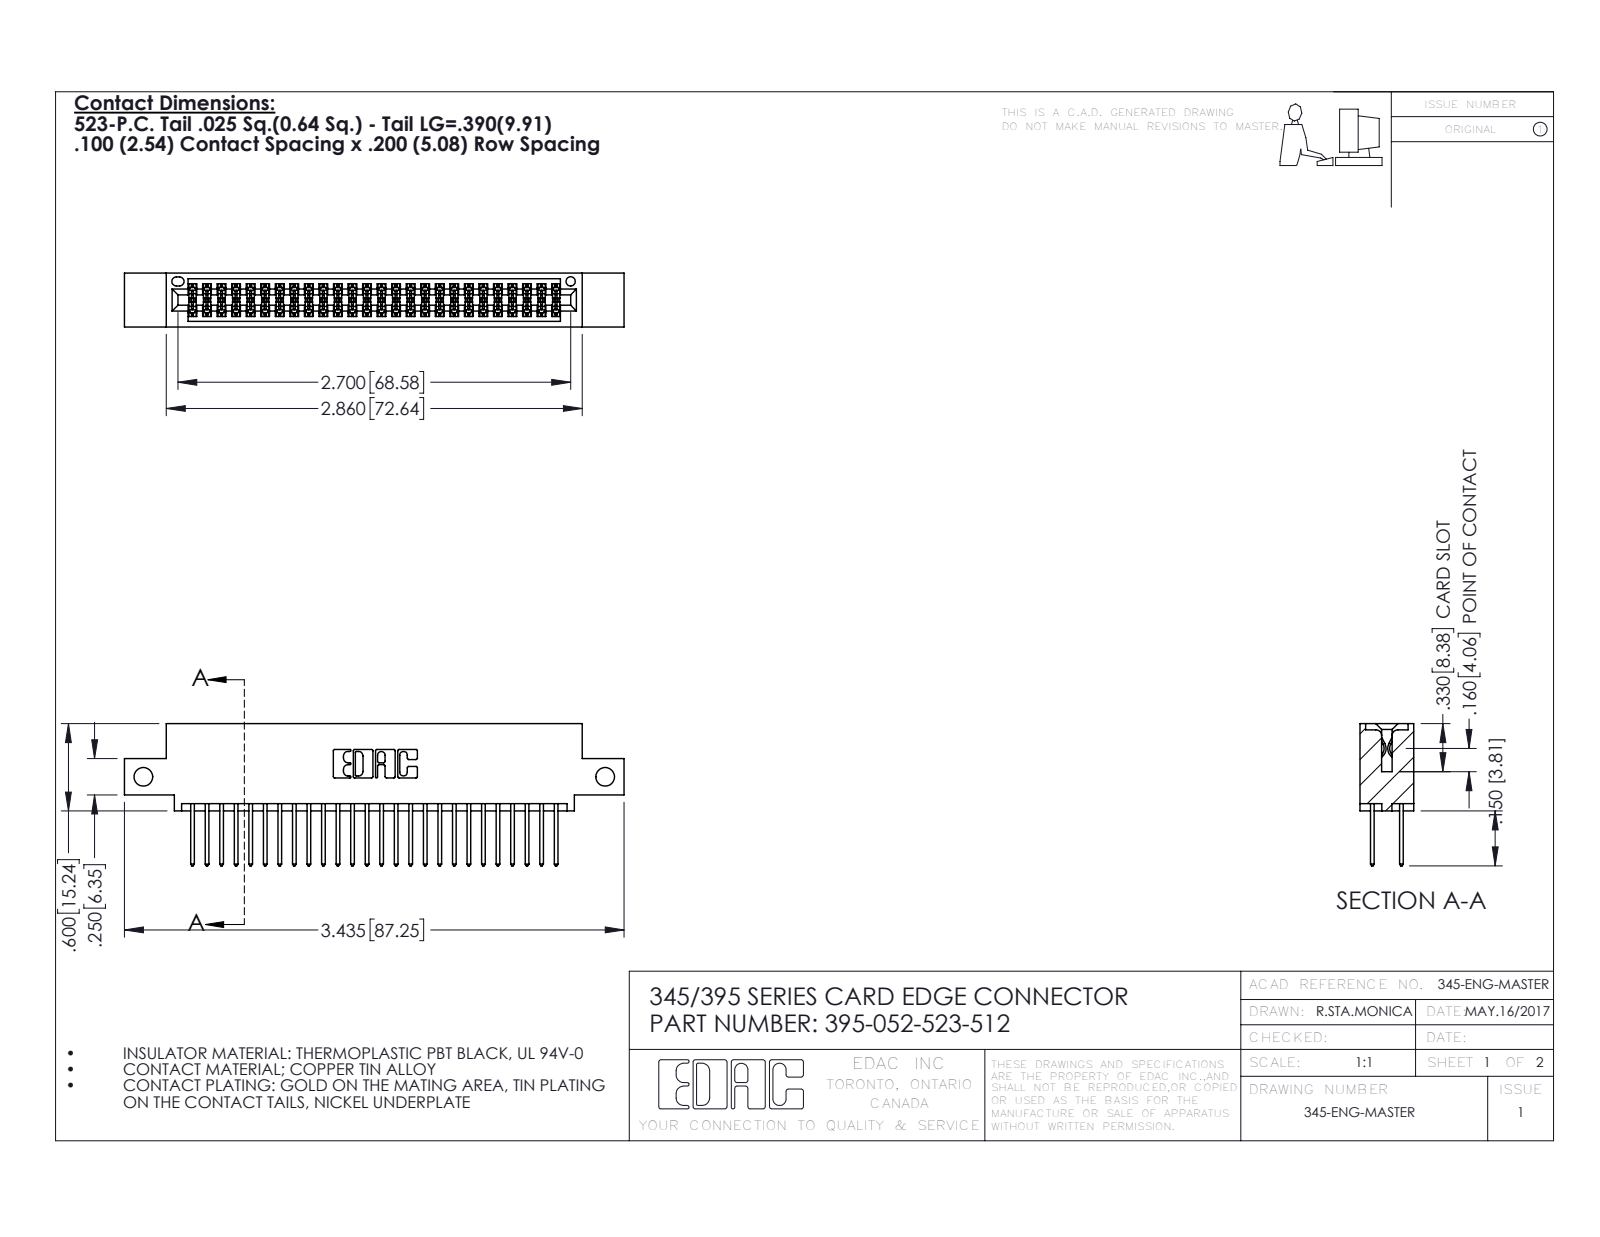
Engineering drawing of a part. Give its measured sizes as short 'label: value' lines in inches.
name: 395-052-523-512; 345 Part_0.110 Offset - Side Mount; 345-292-001_345-293-123
written by: SolidWorks 2016 (CONFIG_CONTROL_DESIGN)
unit: in
bodies: 53 solids, 2730 faces (1800 planar, 930 cylindrical, 0 other)
size: 3.435 × 0.977 × 0.37
volume: 0.505 in³; area: 19.15 in²
holes: 2× ⌀0.128, 1× ⌀0.064
rounds: 78× R0.006, 52× R0.01, 22× R0.01, 6× R0.007, 6× R0.031, 3× R0.026, 2× R0.014, 2× R0.019
face distances: 0.298, 0.072, 0.2, 0.098, 0.272, 0.025, 0.37, 0.225, 0.175, 0.149
hole spacings: 3.175
